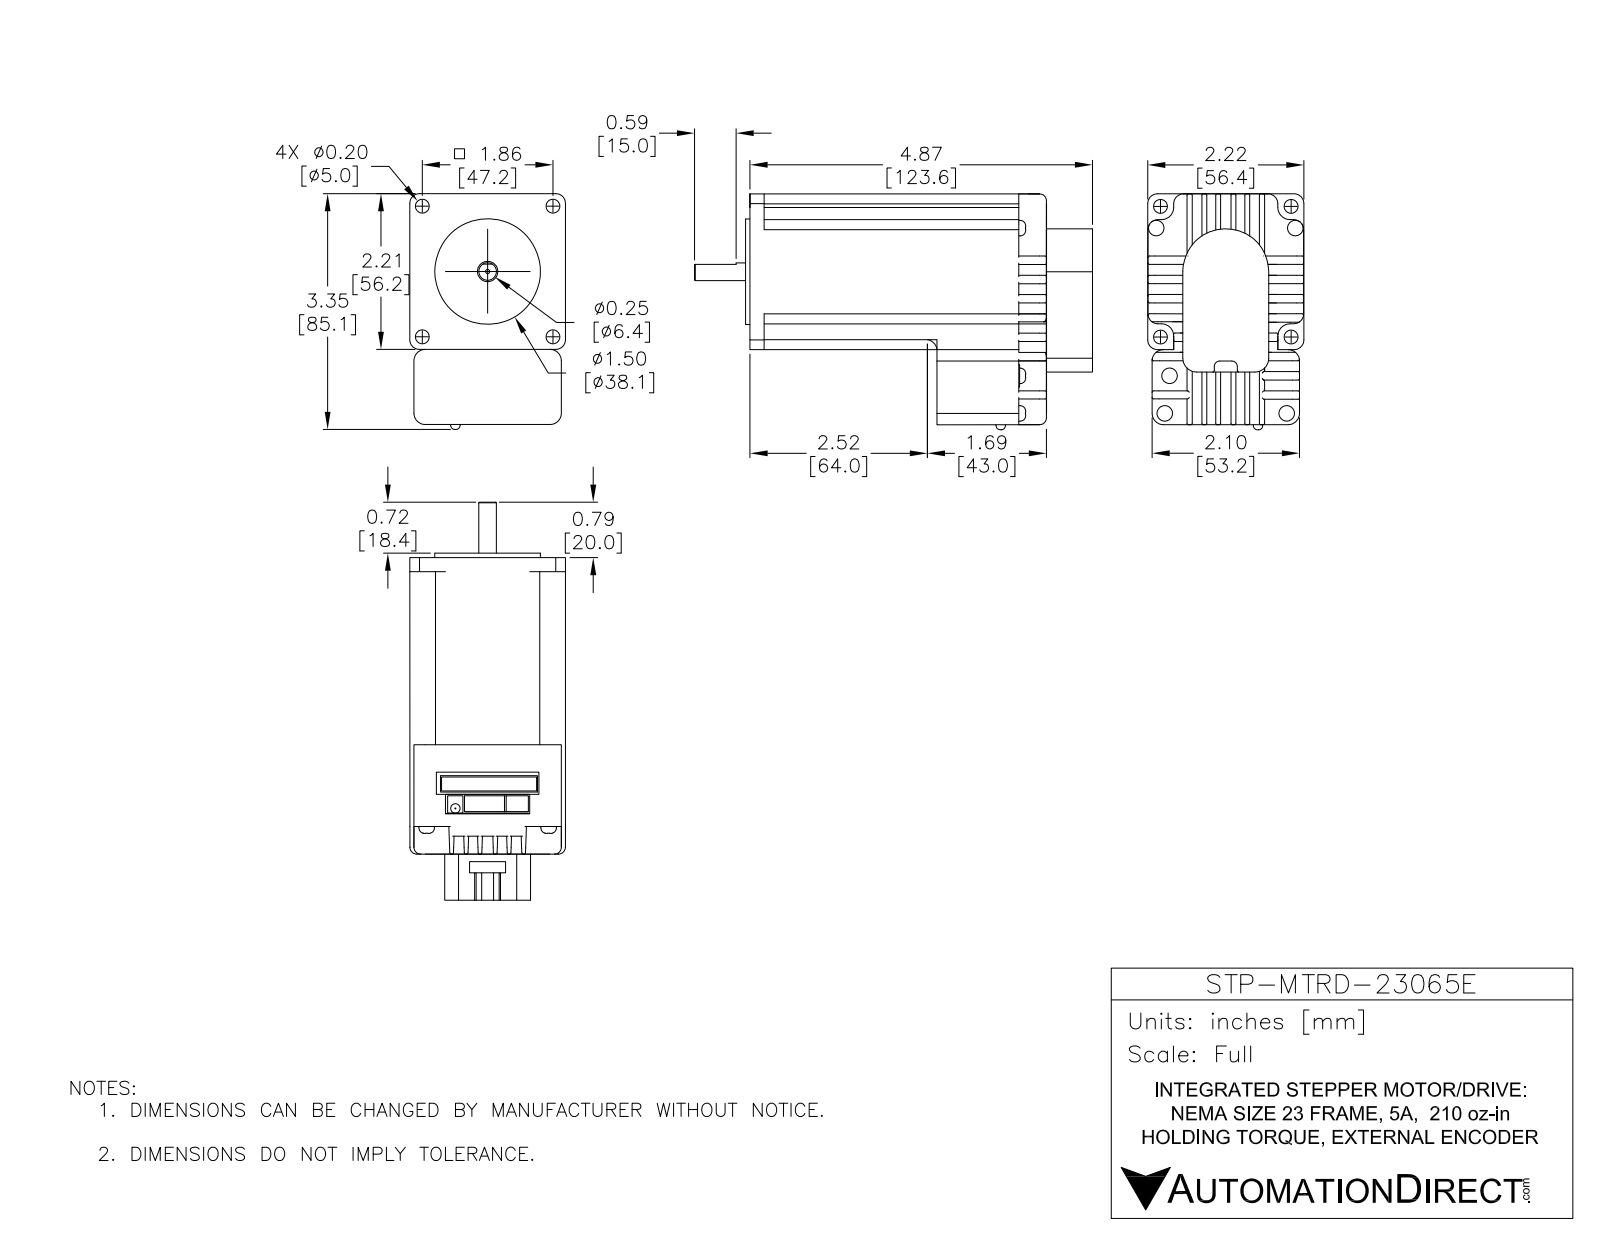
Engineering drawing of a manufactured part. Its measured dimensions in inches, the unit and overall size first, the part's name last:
Units: inches
Overall size (bounding box): 5.654 × 3.339 × 2.213
Round holes (diameter × count): ⌀0.197 ×4, ⌀0.079 ×1, ⌀0.289 ×1, ⌀0.748 ×1
Round bosses / shafts (diameter × count): ⌀0.22 ×5, ⌀0.217 ×4, ⌀1.5 ×1, ⌀0.315 ×1, ⌀0.25 ×1
Partial cylindrical surfaces — rounded edges, fillets, slot ends (radius × count): R0.02 ×87, R0.098 ×10, R0.142 ×8, R0.027 ×5, R0.431 ×5, R0.126 ×4, R0.138 ×4, R0.161 ×4
Main face-to-face distances: 2.213, 0.196, 0.413, 0.394, 0.207, 0.403, 0.62, 0.816, 4.213, 0.909
Hole centre spacings: 1.312, 1.856, 2.625
Volume: 21.94 in³ · Surface area: 78.24 in²
Bodies: 1 solid, 711 faces (331 planar, 259 cylindrical, 121 other)
Part name (STEP PRODUCT): STP-MTRD-23065E
STEP written by: SolidWorks 2017 (AUTOMOTIVE_DESIGN)
